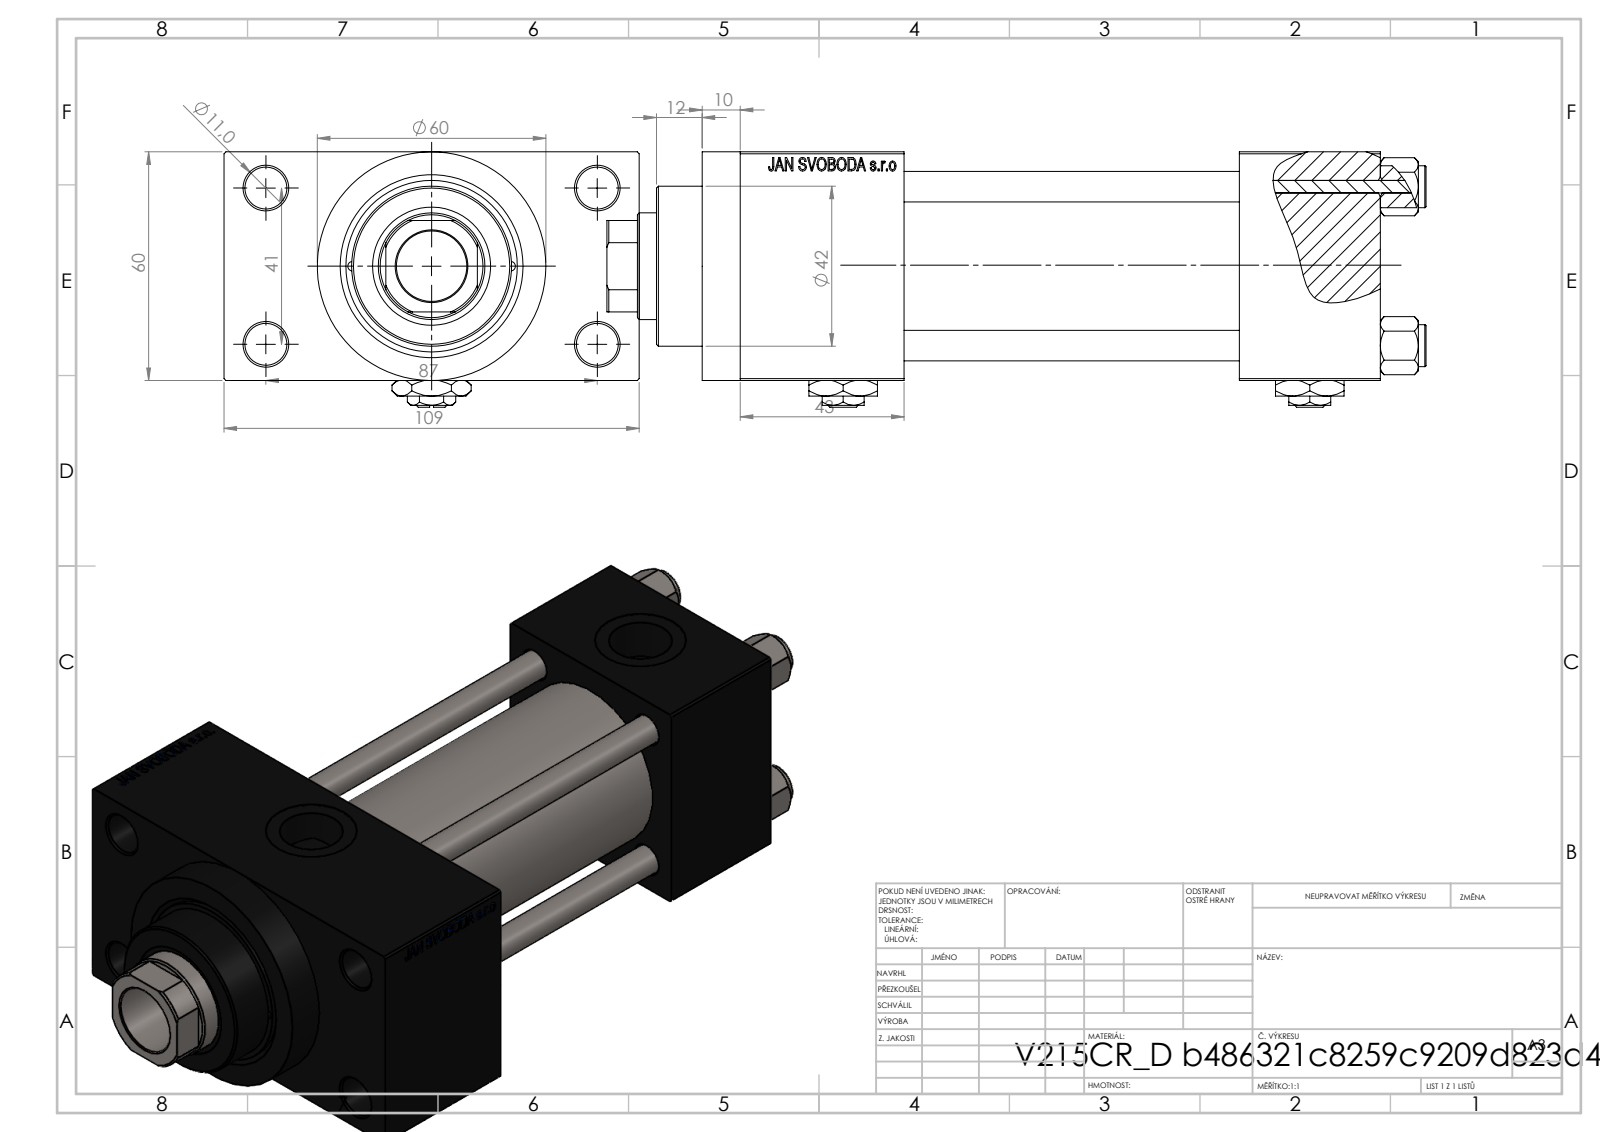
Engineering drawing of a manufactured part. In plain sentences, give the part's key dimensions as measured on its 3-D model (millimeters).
The part is named "V215CR_D_TYCINKA; V215_VC_A; V215CR_VCP_D; Zatka_pro_OIL_PORT (+2 more)". Its 3-D file was written by "SolidWorks 2019 (CONFIG_CONTROL_DESIGN)". It is 13 solids with 1216 faces: 550 planar, 104 cylindrical and 562 other. Overall it measures 215 by 109 by 67 millimeters. Its volume is 568 397 cubic millimeters and its surface area 144 204 square millimeters. Round holes: 4 of diameter 8, 4 of diameter 11, 2 of diameter 2.5, 2 of diameter 7, 2 of diameter 16.66, 2 of diameter 24, 1 of diameter 18.5, 1 of diameter 28, 1 of diameter 31, 1 of diameter 40, 1 of diameter 45. Round bosses or shafts: 4 of diameter 11, 1 of diameter 60, 1 of diameter 46, 1 of diameter 42. Partial cylindrical surfaces (rounded edges, fillets, slot ends): 1 of radius 13.5. The main face-to-face distances are 60, 24.5, 84.5, 88, 37, 125, 168, 131, 43, 109. The hole center spacings are 20.85, 22.65, 29.49, 30.62, 41.7, 46.53, 47.15, 48.09.
